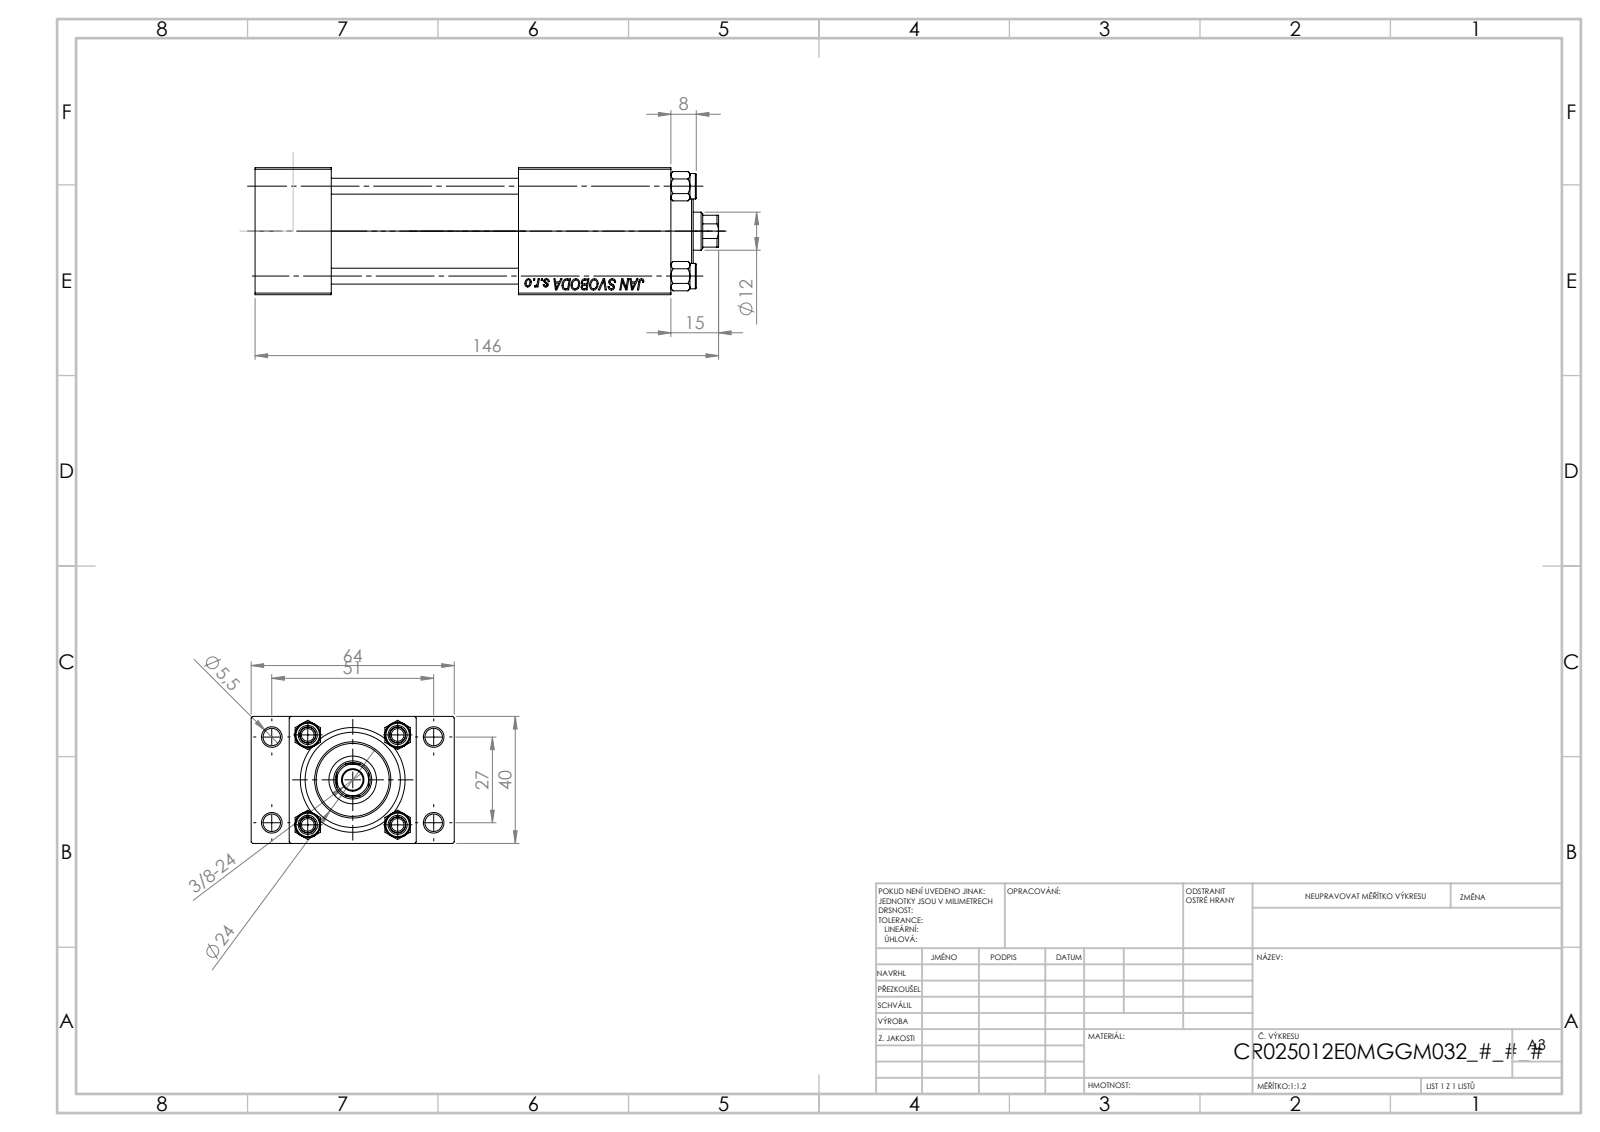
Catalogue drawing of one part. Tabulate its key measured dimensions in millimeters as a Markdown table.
| quantity | value |
| --- | --- |
| part name | V215CR_TYCINKA_E; V215CR_E_Body; V215_VC_A; V215CR_VCP_E (+1 more) |
| STEP written by | SolidWorks 2019 (CONFIG_CONTROL_DESIGN) |
| units | millimeters |
| bodies | 11 solids, 1136 faces (497 planar, 87 cylindrical, 552 other) |
| overall size | 146 × 64 × 40 |
| volume | 169 381 mm³ |
| surface area | 65 422 mm² |
| round holes (diameter × count) | 5 × 4, 5.5 × 4, 20 × 3, 7 × 2, 13.16 × 2, 6.5 × 1, 12 × 1, 15 × 1, 25 × 1, 30 × 1 |
| round bosses / shafts (diameter × count) | 8 × 4, 31 × 1, 24 × 1 |
| partial cylindrical surfaces (radius × count) | 5.5 × 1 |
| main face-to-face distances | 40, 24, 12, 52, 131, 107, 102.3, 78.3, 28.7, 64 |
| hole center spacings | 11.37, 20.01, 28.3, 28.85, 29.89, 39.66, 48.34, 27 |
